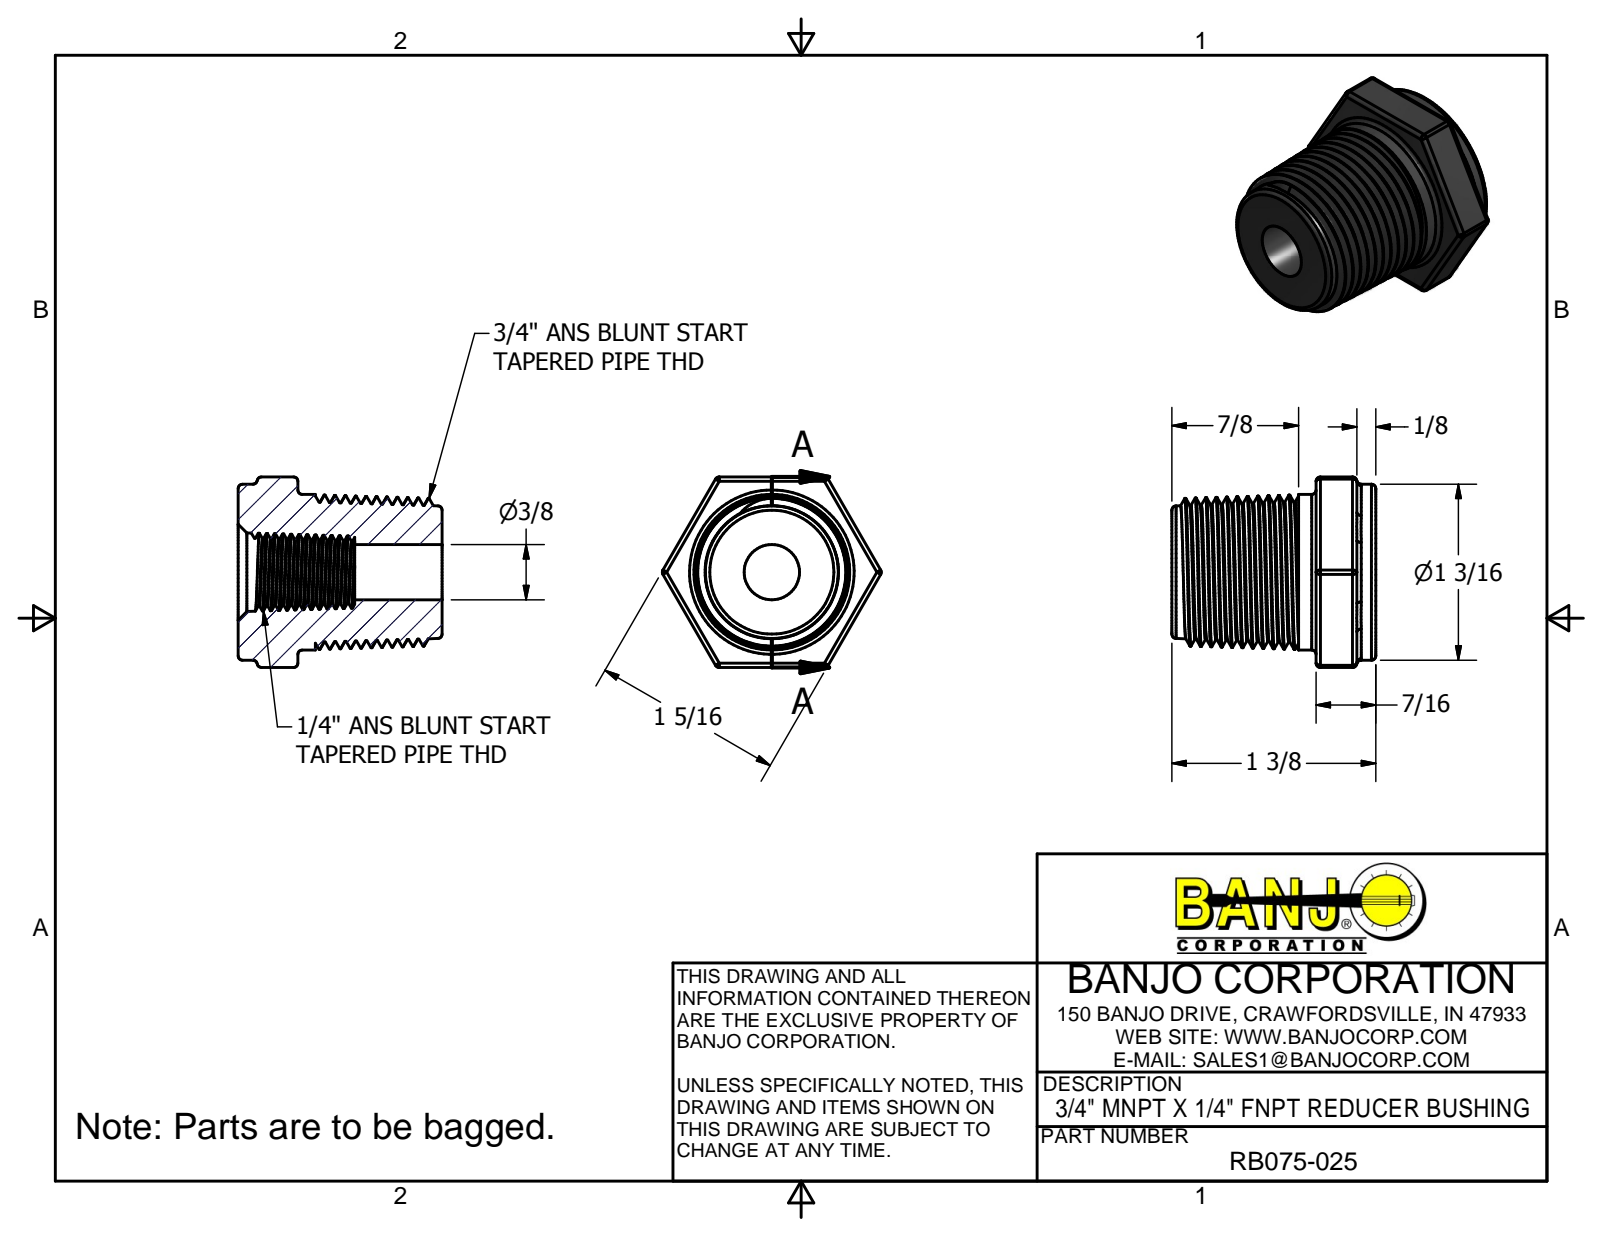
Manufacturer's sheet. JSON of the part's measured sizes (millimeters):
{"part_name": "RB075-025", "step_written_by": "Autodesk Inventor 2014 (AUTOMOTIVE_DESIGN)", "units": "millimeters", "bodies": {"solids": 1, "faces": 104, "planar": 17, "cylindrical": 24, "other": 63}, "overall_size": [38.19, 35.56, 33.27], "volume_mm3": 18152, "surface_area_mm2": 7548, "round_holes": [[9.65, 1]], "round_bosses_or_shafts": [[30.73, 1], [27.18, 1]], "partial_cylinders_radius": [[0.76, 18], [4.36, 1], [7.09, 1]], "face_to_face_distances": [33.28, 35.56, 10.41, 25.15, 3.3, 7.11, 32.26, 13.46, 10.16, 3.05]}
